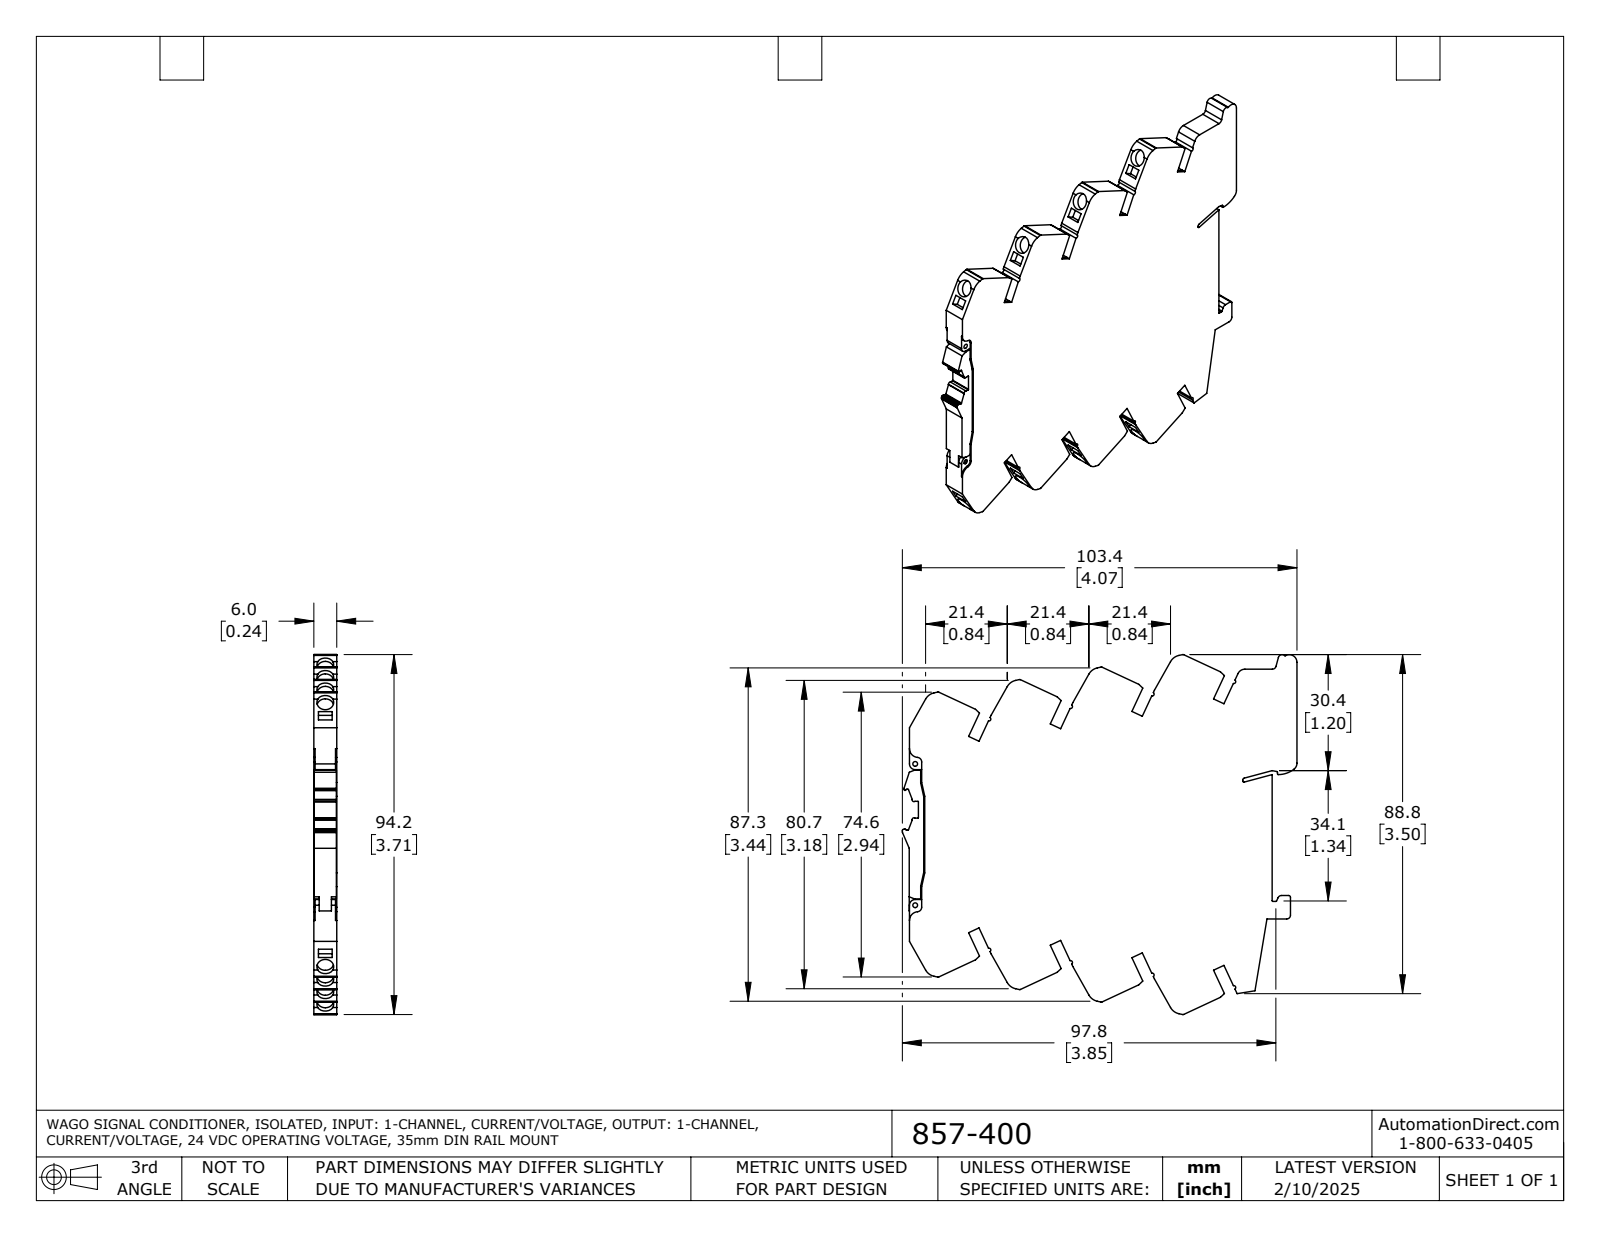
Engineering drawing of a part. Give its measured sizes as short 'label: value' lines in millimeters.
name: 857-400
written by: SolidWorks 2021 (AUTOMOTIVE_DESIGN)
unit: mm
bodies: 1 solid, 317 faces (219 planar, 98 cylindrical, 0 other)
size: 103.4 × 94.3 × 6
volume: 43 930 mm³; area: 19 260 mm²
holes: 8× ⌀4.4, 2× ⌀1.2
rounds: 12× R0.5, 11× R0.2, 8× R0.4, 8× R3.4, 4× R1, 3× R0.3, 3× R2, 2× R0.5
face distances: 6, 18, 17, 12, 5.9, 12, 3, 24, 36, 6.5
hole spacings: 13.4, 13.3, 26.7, 26.7, 26.7, 37, 40, 40.1
